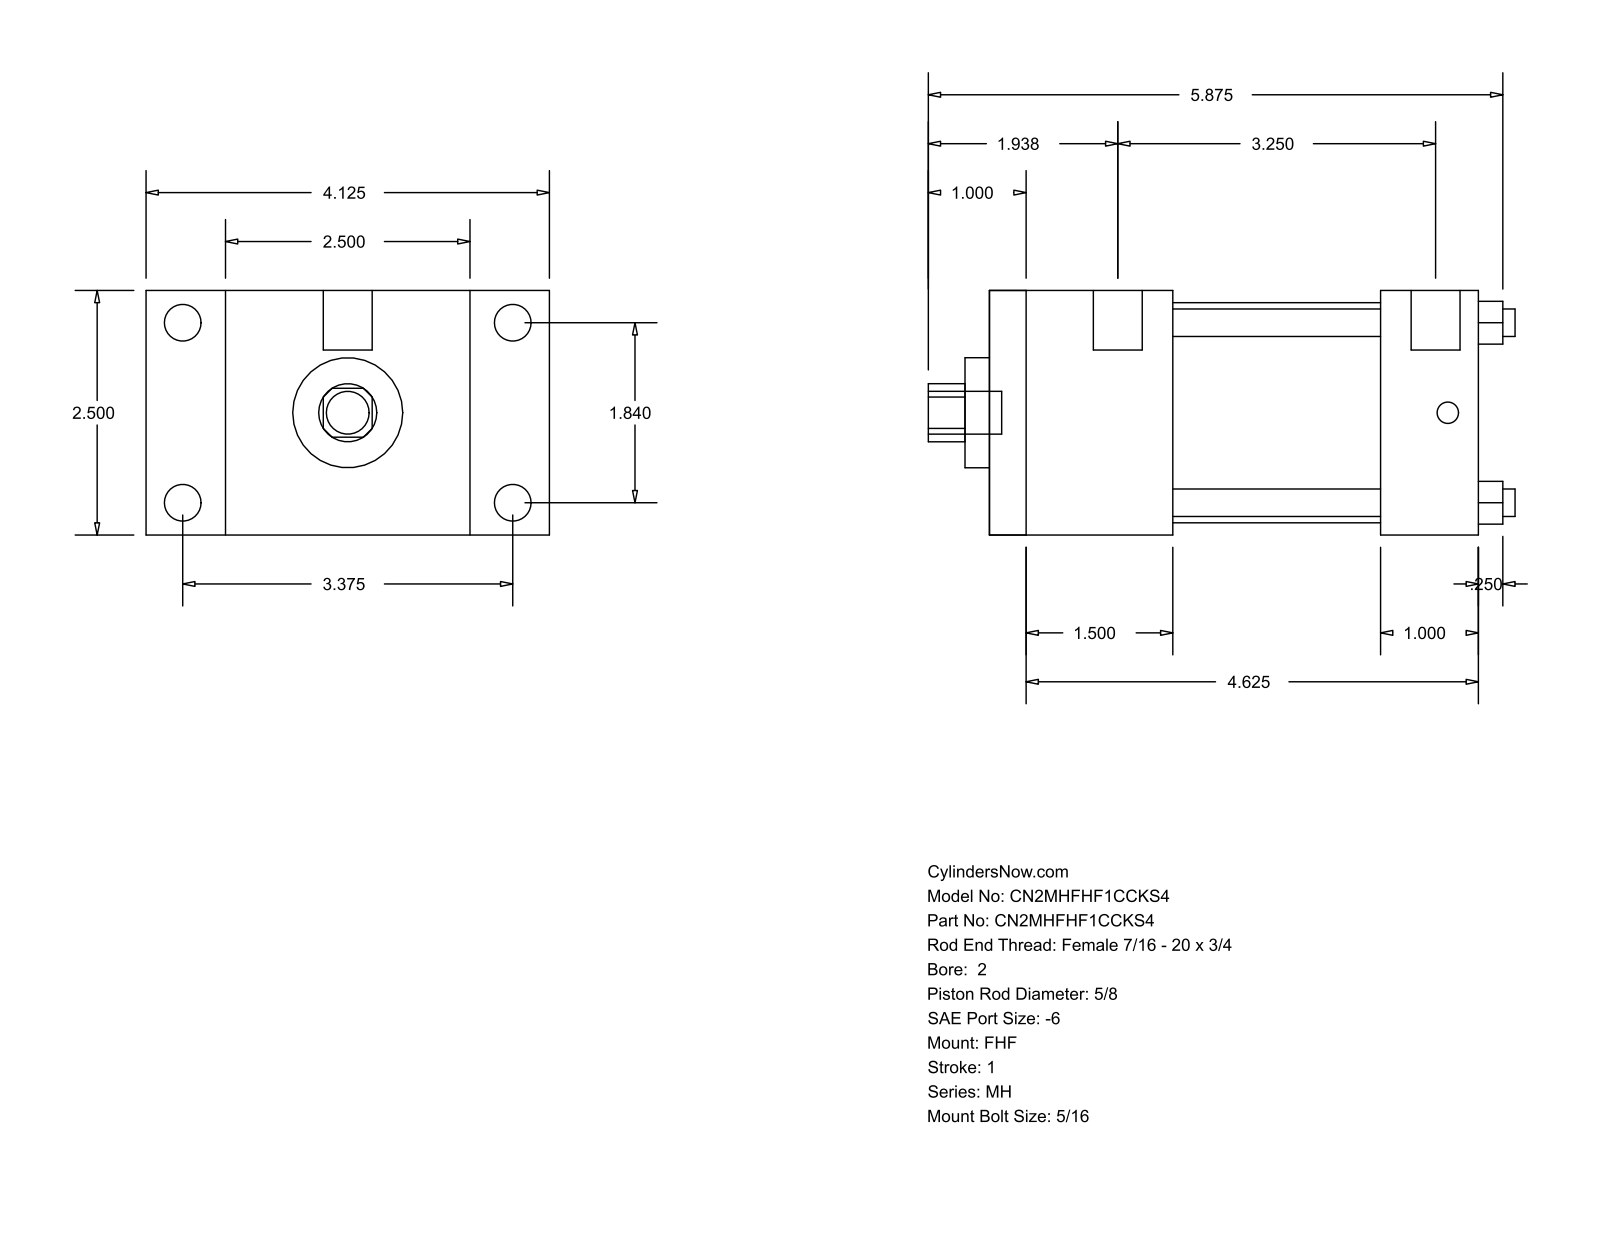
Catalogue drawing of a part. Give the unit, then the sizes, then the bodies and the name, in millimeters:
Units: millimetres
Overall size (bounding box): 152.4 × 104.78 × 63.5
Round holes (diameter × count): ⌀7.14 ×4, ⌀15.88 ×1, ⌀28.57 ×1, ⌀57.15 ×1
Round bosses / shafts (diameter × count): ⌀9.53 ×4, ⌀5.56 ×4, ⌀12.7 ×2, ⌀11.11 ×1
Partial cylindrical surfaces — rounded edges, fillets, slot ends (radius × count): R7.54 ×1
Main face-to-face distances: 63.5, 47.62, 127, 79.38, 20.64, 84.14, 104.78, 53.97, 101.59, 25.41
Hole centre spacings: 33.05, 46.74, 66.1
Bodies: 0 solids, 88 faces (60 planar, 28 cylindrical, 0 other)
Part name (STEP PRODUCT): MH_FHF__0200_0.625
STEP written by: GSSL Pune (CONFIG_CONTROL_DESIGN)
